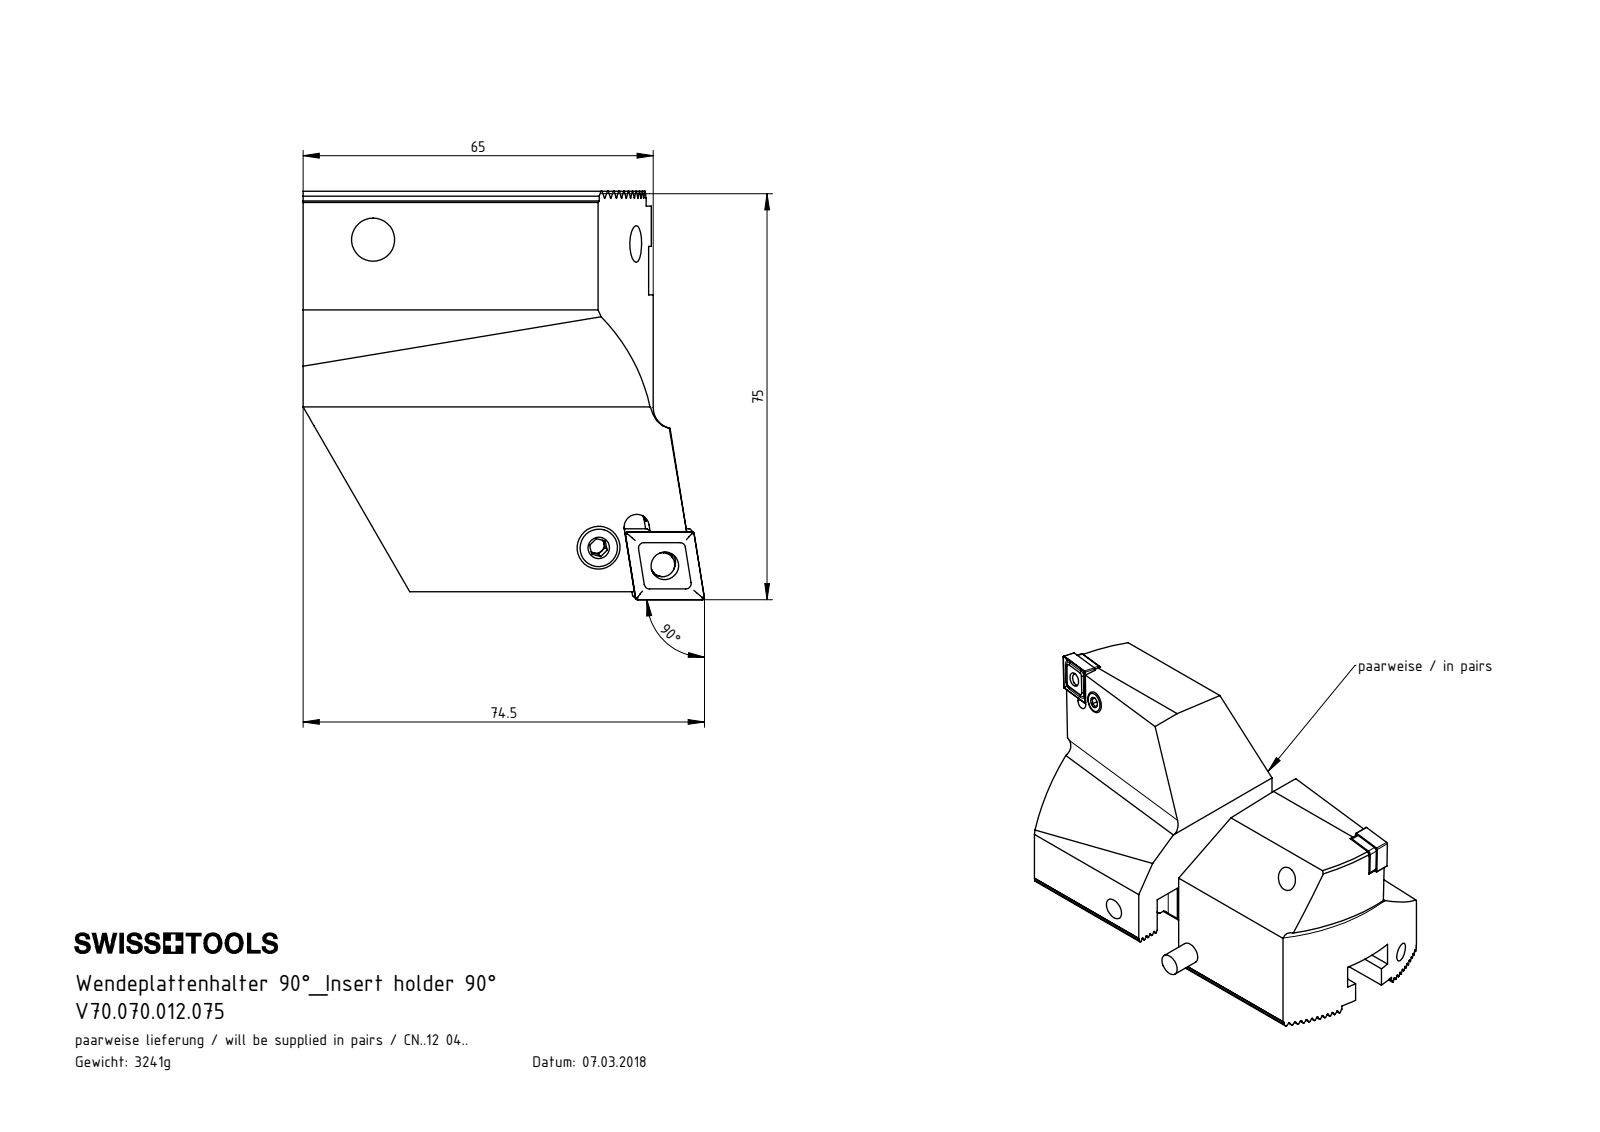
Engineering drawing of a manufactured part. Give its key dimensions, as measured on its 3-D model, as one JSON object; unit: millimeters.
{"part_name": "WCD; WCD-ER2.101.003_A; CNMG120404; ISO 8734 - 8 x 20 m6 (+5 more)", "step_written_by": "SolidWorks 2017 (AUTOMOTIVE_DESIGN)", "units": "millimeters", "bodies": {"solids": 7, "faces": 278, "planar": 160, "cylindrical": 60, "other": 58}, "overall_size": [82, 75.79, 74.51], "volume_mm3": 205611, "surface_area_mm2": 32774, "round_holes": [[8, 2], [5.16, 1], [6.4, 1], [6.8, 1], [7, 1], [8.4, 1]], "round_bosses_or_shafts": [[8, 1], [7.9, 1], [6.4, 1], [4.5, 1], [3.55, 1]], "partial_cylinders_radius": [[0.14, 22], [0.4, 4], [1, 4], [2.5, 3], [2.1, 1], [2.2, 1], [2.35, 1], [2.8, 1]], "face_to_face_distances": [1.73, 8.66, 3.46, 6.93, 43.3, 10.39, 41.57, 24.5, 45.5, 5.2], "hole_center_spacings": [7, 12.8, 12.86]}
